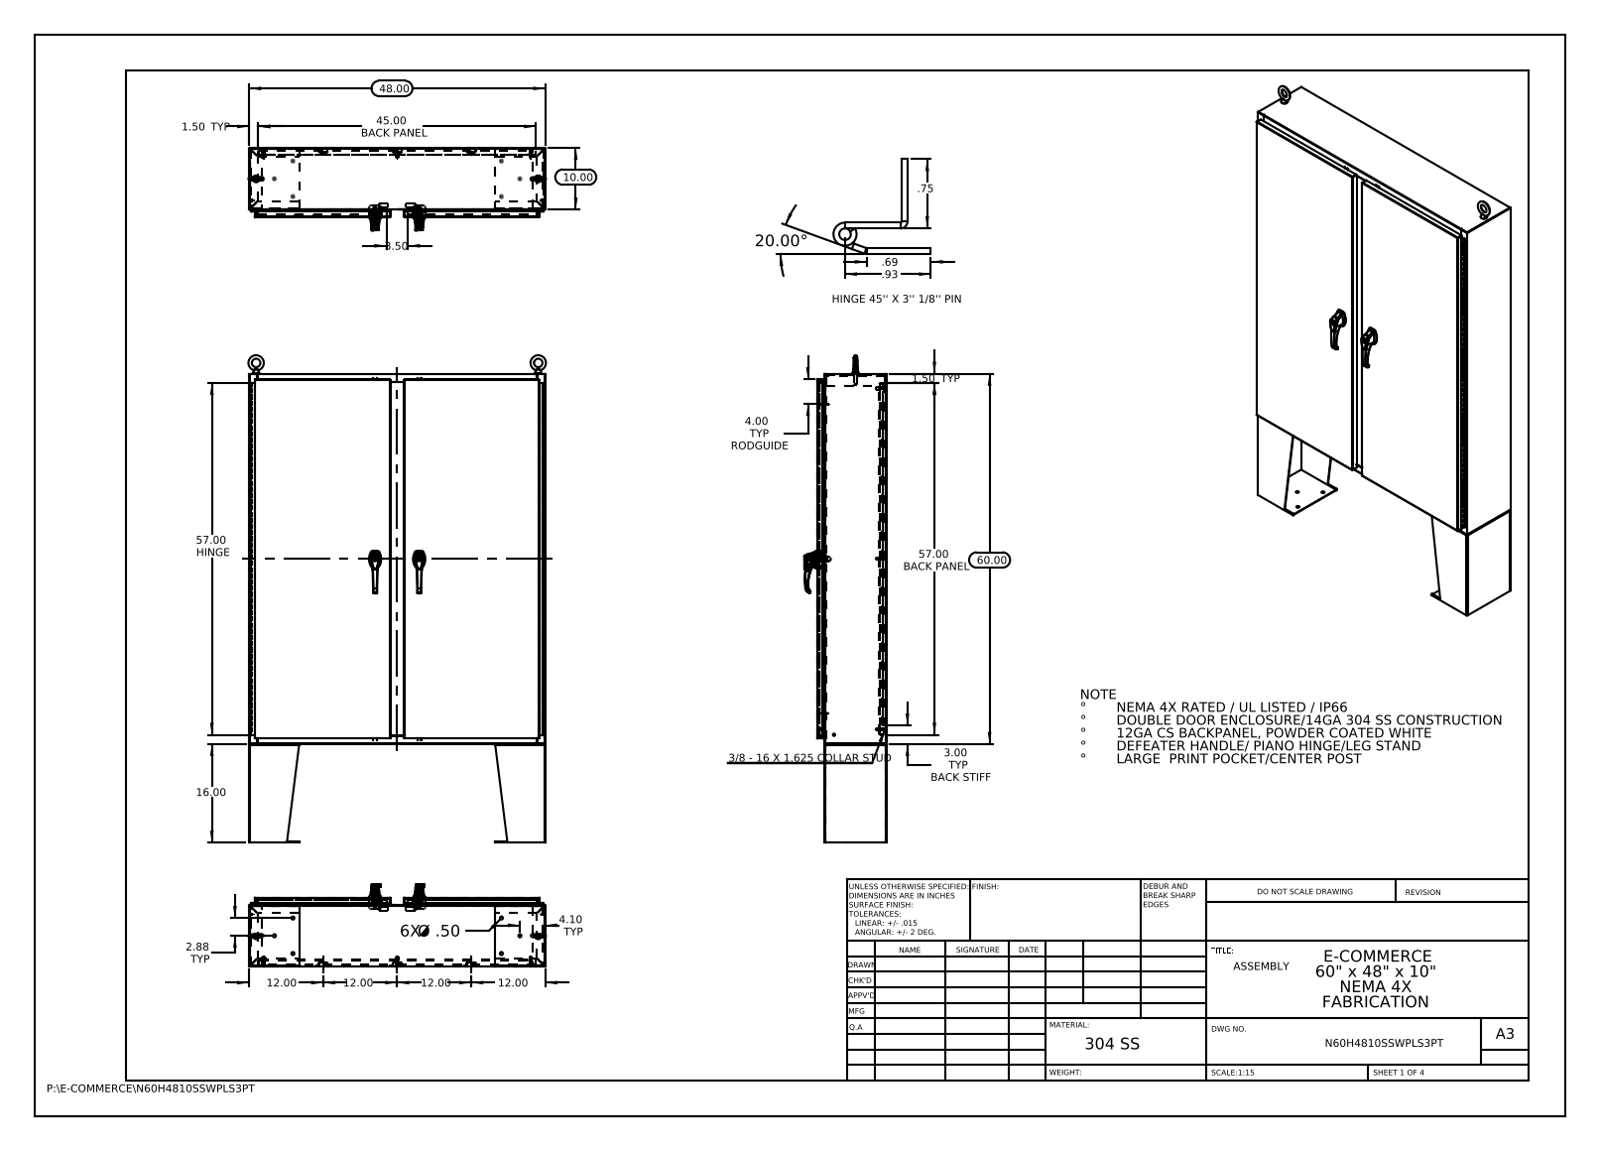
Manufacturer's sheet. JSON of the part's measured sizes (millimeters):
{"part_name": "N60H4810SSWPLS3PT Bottom; N60H4810SSWPLS3PT; N60H4810SSWPLS3PT DD_Leg Kit; 022151 (+8 more)", "step_written_by": "SolidWorks 2013 (CONFIG_CONTROL_DESIGN)", "units": "millimeters", "bodies": {"solids": 66, "faces": 6660, "planar": 2654, "cylindrical": 2642, "other": 1364}, "overall_size": [2006.6, 1224.9, 338], "volume_mm3": 18580000, "surface_area_mm2": 17650000, "round_holes": [[12.7, 14], [6.4, 8], [3.5, 6], [4.1, 6], [2, 4], [8, 4], [11.1, 4], [19.1, 4], [3.2, 2], [3.2, 2], [5, 2], [5.2, 2]], "round_bosses_or_shafts": [[15.9, 10], [9.5, 8], [8.4, 8], [8, 5], [6, 5], [30, 2], [19, 2], [17.3, 2]], "partial_cylinders_radius": [[3, 72], [0.2, 66], [0.3, 44], [2.2, 36], [1, 28], [0.7, 24], [0.2, 12], [0.5, 12]], "face_to_face_distances": [1.9, 282.6, 2.6, 27.3, 280.7, 25.4, 255.3, 29.9, 28, 252.7], "hole_center_spacings": [181.7, 181.8, 181.8, 593.5, 652.1, 7.5, 15.9, 21.4]}
